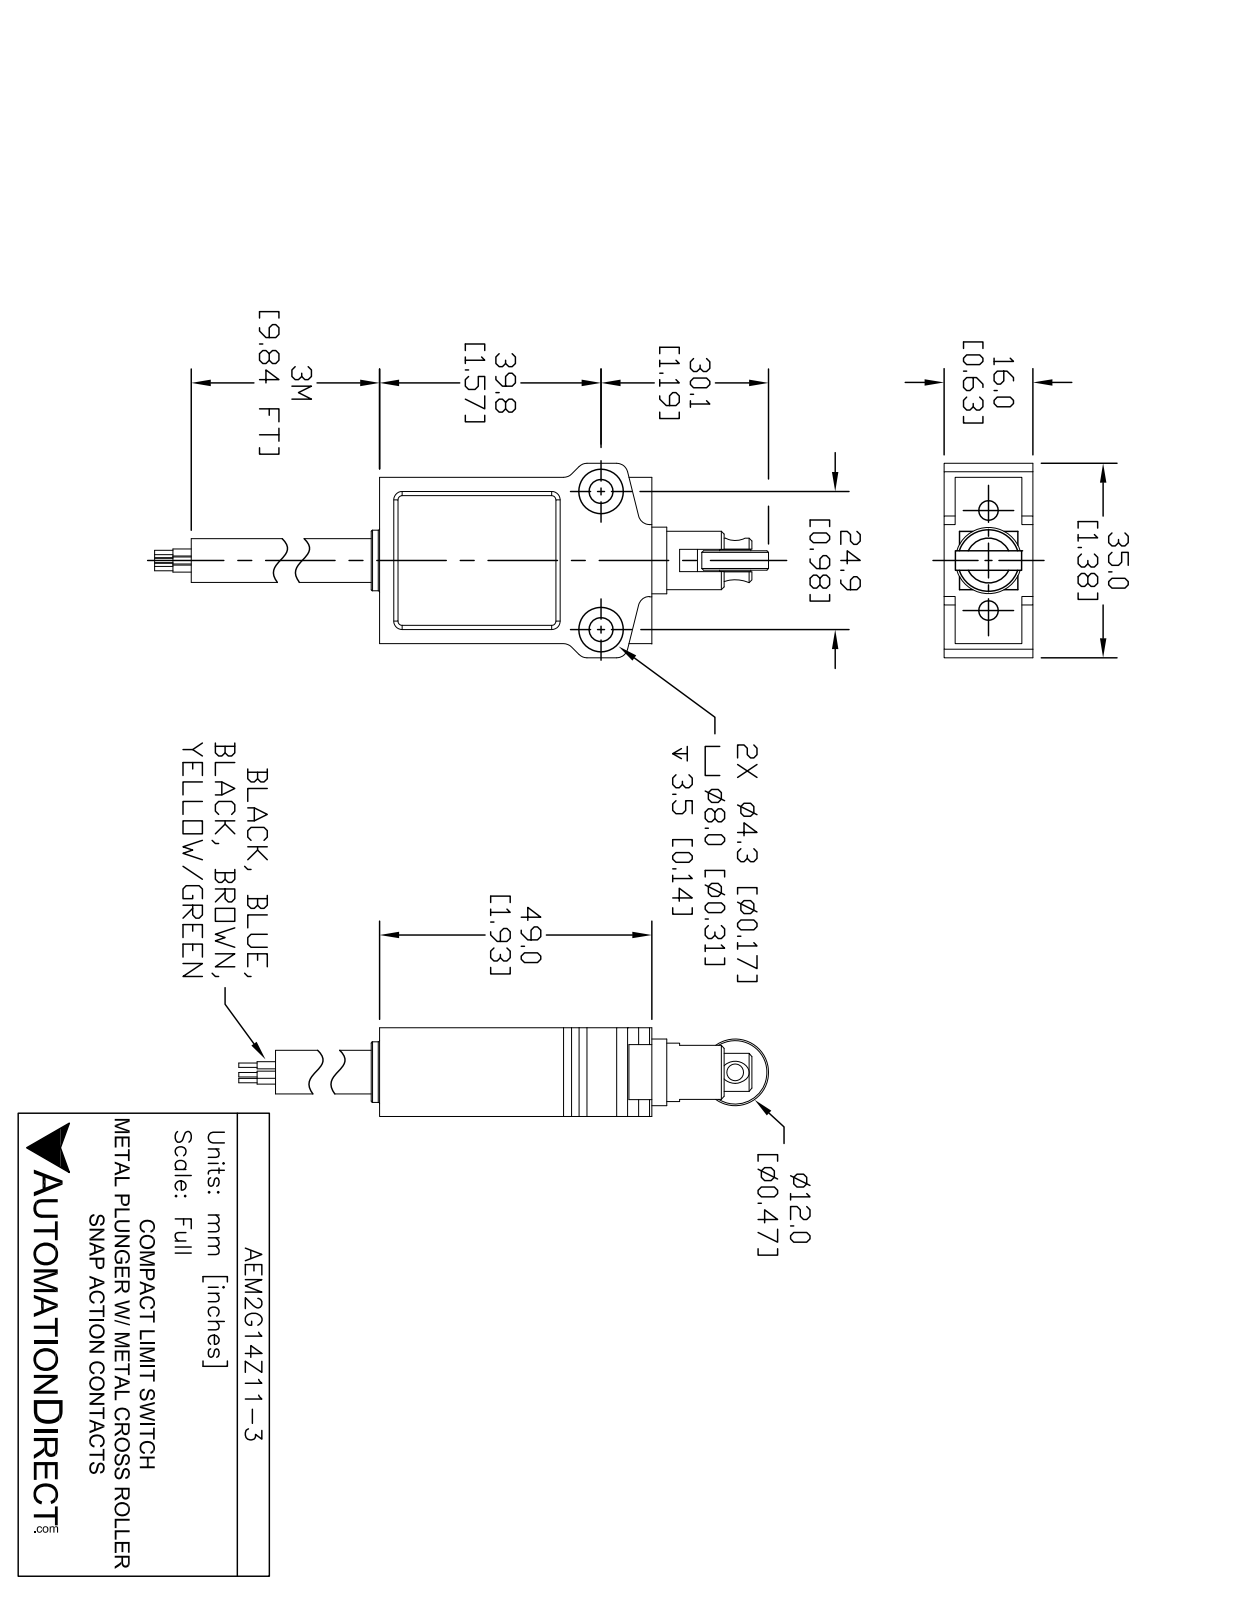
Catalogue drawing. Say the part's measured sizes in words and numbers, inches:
The part is named "AEM2G14Z11-3_Default". Its 3-D file was written by "SolidWorks 2021 (CONFIG_CONTROL_DESIGN)". It is 2 solids with 119 faces: 56 planar, 43 cylindrical and 20 other. Overall it measures 3.385 by 1.38 by 0.63 inches. Its volume is 1.426 cubic inches and its surface area 11.99 square inches. Round holes: 2 of diameter 0.138, 2 of diameter 0.177, 2 of diameter 0.344. Round bosses or shafts: 5 of diameter 0.05, 5 of diameter 0.031, 2 of diameter 0.47, 1 of diameter 0.43, 1 of diameter 0.41, 1 of diameter 0.31. Partial cylindrical surfaces (rounded edges, fillets, slot ends): 8 of radius 0.03, 8 of radius 0.08, 1 of radius 0.135. The main face-to-face distances are 0.03, 0.6, 0.57, 0.63, 1.18, 1.93, 0.51, 0.67, 0.505, 0.675. The hole center spacings are 0.7, 0.98.
